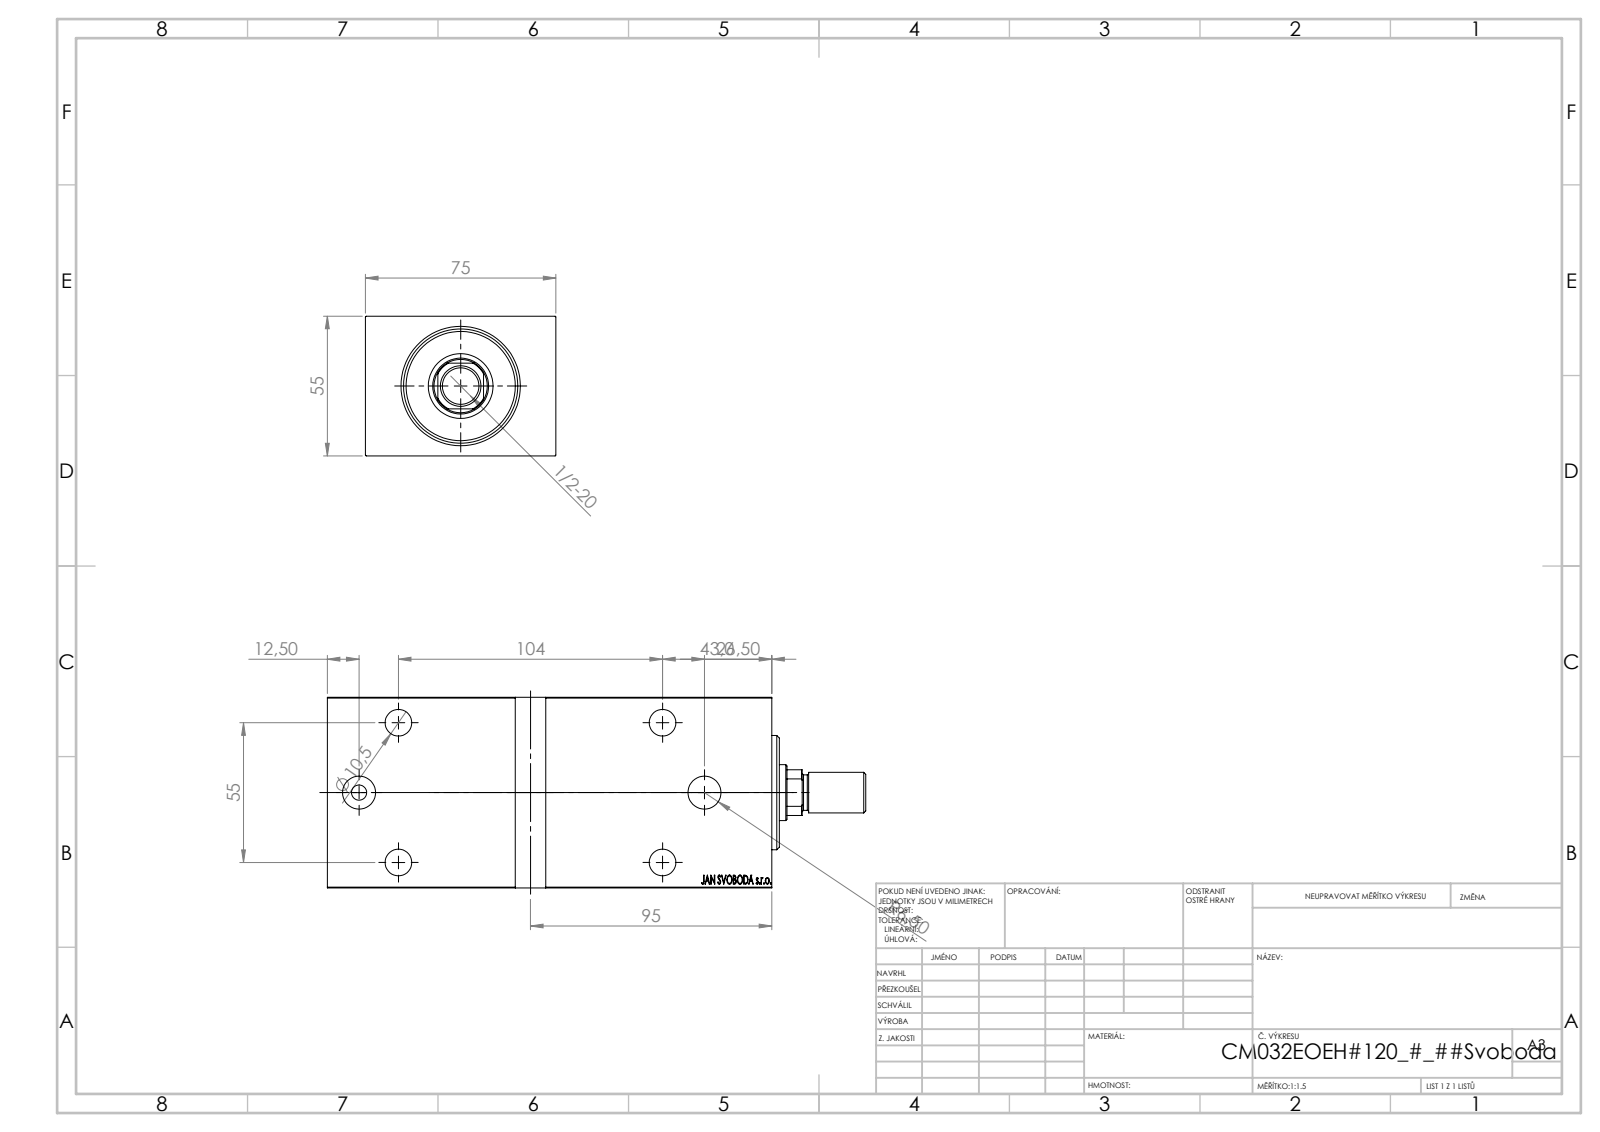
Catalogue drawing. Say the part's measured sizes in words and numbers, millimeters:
The part is named "V450CM_E_Body; V450CM_VC_B; V450CM_E_VCP; V450CM_MALE_METRIC". Its 3-D file was written by "SolidWorks 2019 (CONFIG_CONTROL_DESIGN)". It is 4 solids with 859 faces: 411 planar, 48 cylindrical and 400 other. Overall it measures 212 by 75 by 55 millimeters. Its volume is 654 674 cubic millimeters and its surface area 101 846 square millimeters. Round holes: 5 of diameter 10.5, 4 of diameter 16.5, 2 of diameter 13, 1 of diameter 22, 1 of diameter 25.5, 1 of diameter 32, 1 of diameter 45. Round bosses or shafts: 1 of diameter 34, 1 of diameter 16, 1 of diameter 14, 1 of diameter 6. Partial cylindrical surfaces (rounded edges, fillets, slot ends): 1 of radius 10.5. The main face-to-face distances are 55, 75, 175, 3, 10, 165, 5, 170, 160, 178. The hole center spacings are 31.57, 32.07, 55, 104, 117.65, 122.62, 123.6, 136.
